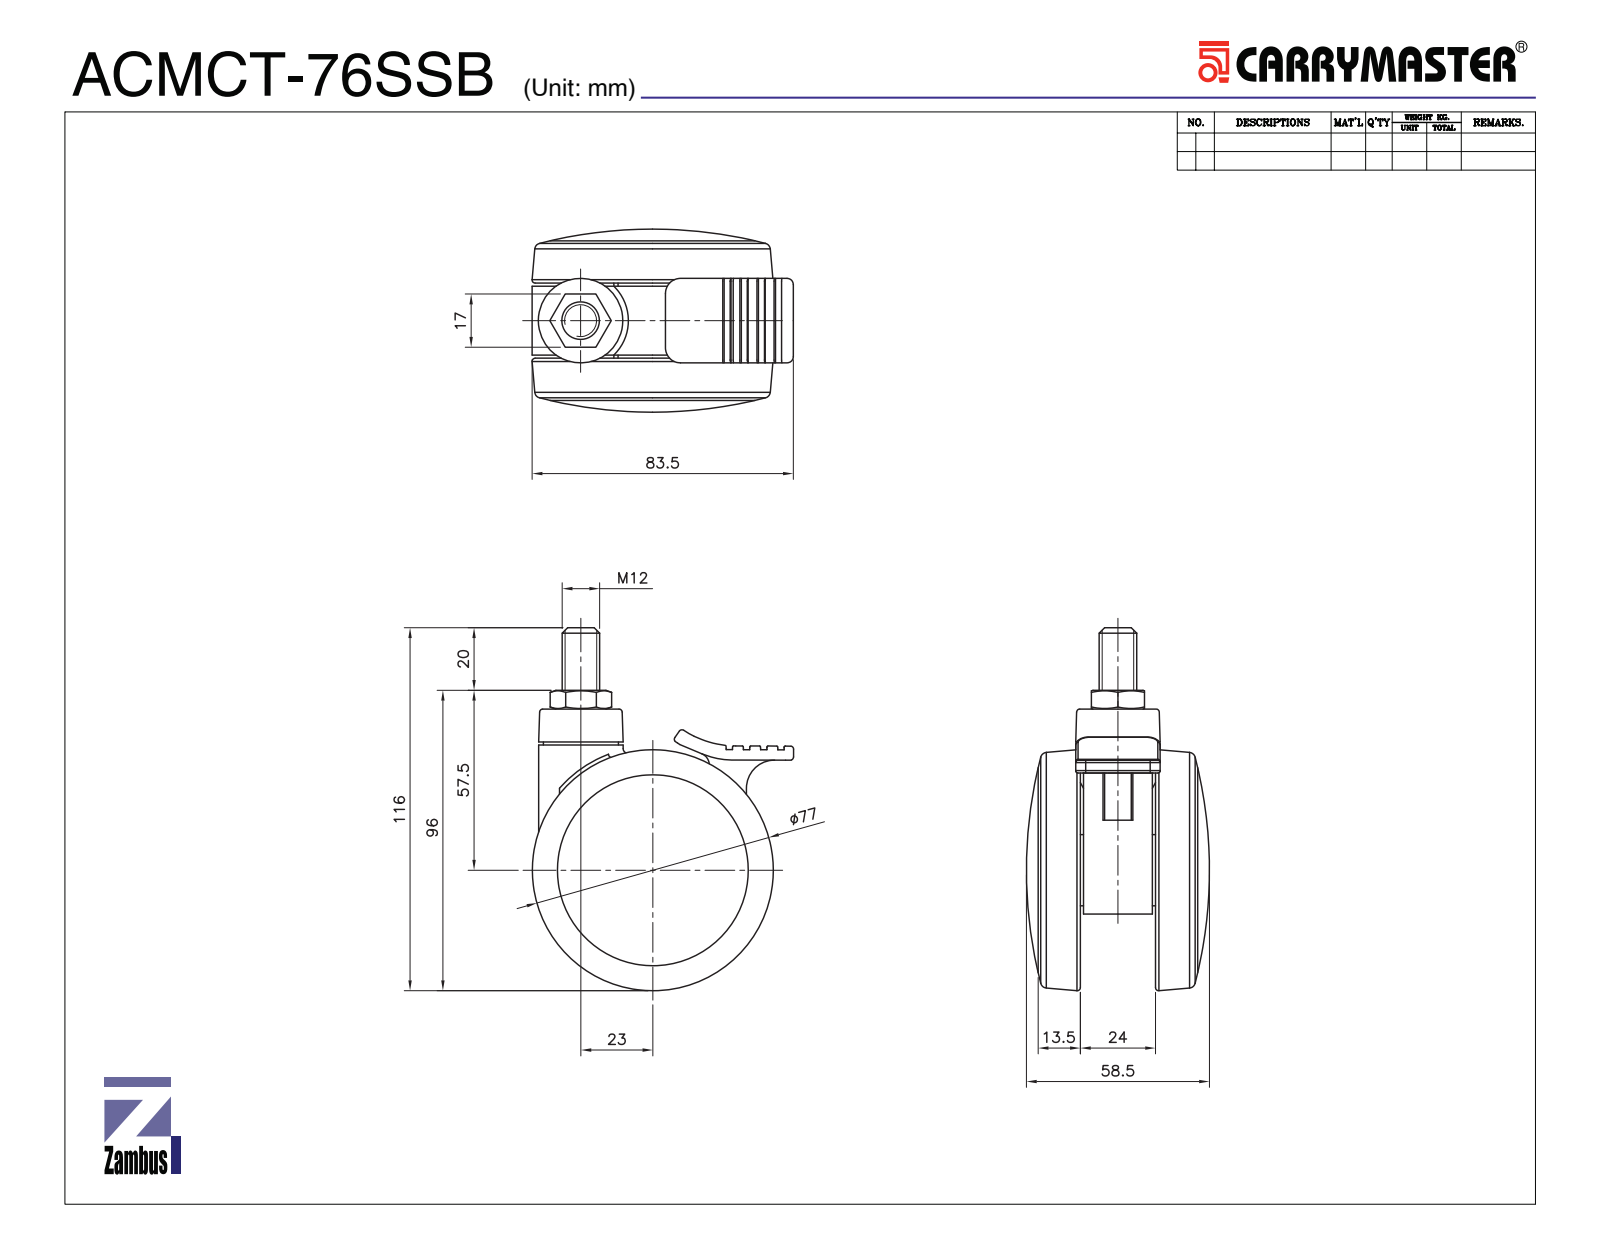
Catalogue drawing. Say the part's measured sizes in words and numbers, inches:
The part is named "ACMCT_76SSB_3D; ACMC-76 BRAKE; ACMC-76 BOLT; 76 BRAKE TYPE FRAME (+2 more)". Its 3-D file was written by "SolidWorks 2020 (CONFIG_CONTROL_DESIGN)". It is 6 solids with 428 faces: 143 planar, 196 cylindrical and 89 other. Overall it measures 4.547 by 3.287 by 2.303 inches. Its volume is 11.07 cubic inches and its surface area 82.85 square inches. Round holes: 1 of diameter 0.591, 1 of diameter 2.165, 1 of diameter 2.409. Round bosses or shafts: 1 of diameter 2.402, 1 of diameter 1.063, 1 of diameter 0.945, 1 of diameter 0.866, 1 of diameter 0.65, 1 of diameter 0.512, 1 of diameter 0.404, 1 of diameter 0.236. Partial cylindrical surfaces (rounded edges, fillets, slot ends): 40 of radius 0.012, 12 of radius 0.008, 8 of radius 0.039, 4 of radius 0.079, 3 of radius 0.157, 1 of radius 0.335, 1 of radius 0.354, 1 of radius 1.161. The main face-to-face distances are 0.433, 1.299, 0.866, 1.732, 0.177, 0.689, 0.787, 0.61, 0.256, 1.043.
